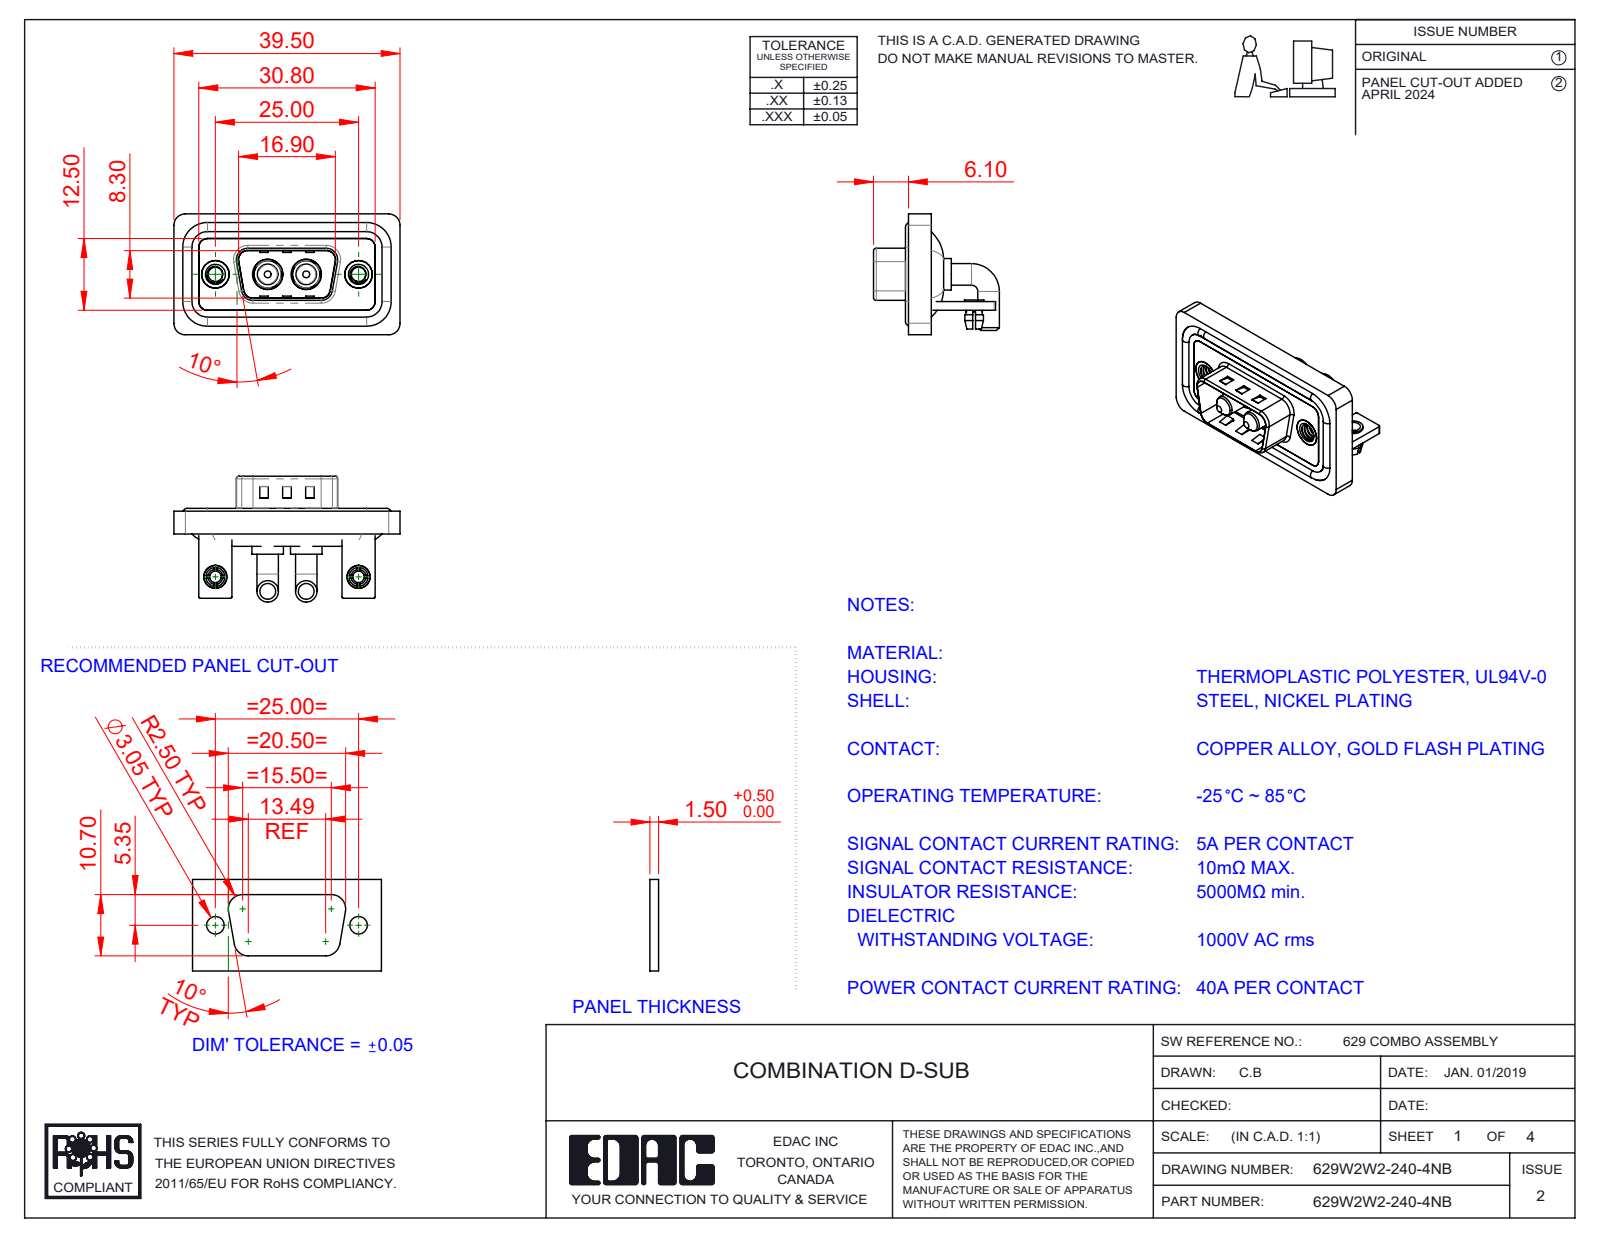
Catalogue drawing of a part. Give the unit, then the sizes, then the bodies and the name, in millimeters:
Units: millimetres
Overall size (bounding box): 39.5 × 21.98 × 21.1
Round holes (diameter × count): ⌀2.5 ×4, ⌀2 ×2, ⌀3.2 ×2, ⌀4 ×2, ⌀4.8 ×2, ⌀4.85 ×2, ⌀5 ×2, ⌀5.3 ×2
Round bosses / shafts (diameter × count): ⌀3.75 ×4, ⌀1.6 ×4, ⌀5.5 ×2, ⌀5.2 ×2, ⌀4.9 ×2, ⌀4.75 ×2, ⌀4 ×2, ⌀3.6 ×2
Partial cylindrical surfaces — rounded edges, fillets, slot ends (radius × count): R2 ×19, R1.5 ×18, R0.25 ×16, R0.5 ×9, R1.6 ×8, R0.6 ×4, R0.65 ×4, R0.9 ×4
Main face-to-face distances: 0.4, 1.5, 2.9, 0.8, 1.1, 1.2, 2.1, 1.6, 3.7, 2.5
Hole centre spacings: 9.14, 15.86, 25, 6.72
Volume: 5 038 mm³ · Surface area: 8 054 mm²
Bodies: 15 solids, 627 faces (233 planar, 272 cylindrical, 122 other)
Part name (STEP PRODUCT): 629Combo Threaded Rivet_B; 629Combo Stabilizer Bracket; 629Combo Shell Front_09 Contacts; 629Combo Shell Rear_09 Contacts (+5 more)
STEP written by: SolidWorks 2023 (CONFIG_CONTROL_DESIGN)
